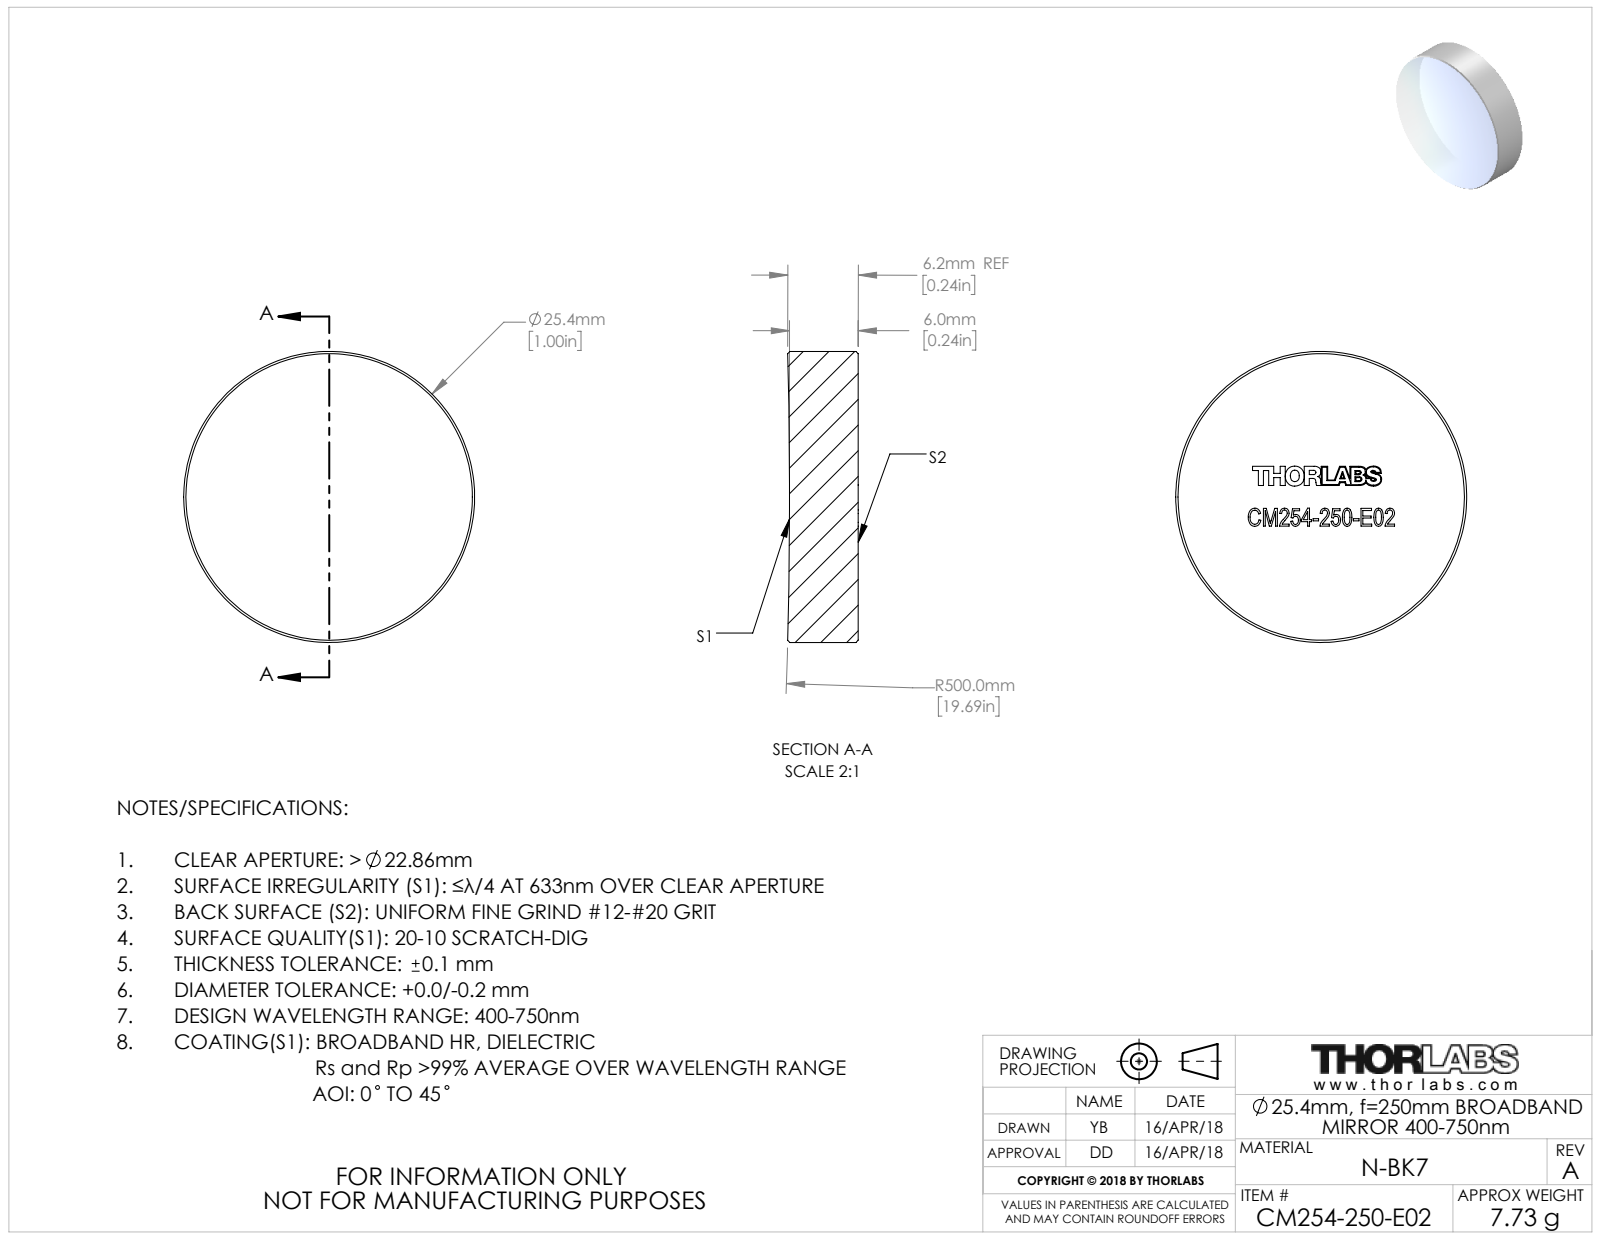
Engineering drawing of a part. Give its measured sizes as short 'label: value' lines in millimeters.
name: TTN153299-E0W
written by: SolidWorks 2018 (CONFIG_CONTROL_DESIGN)
unit: mm
bodies: 1 solid, 40 faces (32 planar, 2 cylindrical, 6 other)
size: 25.4 × 25.4 × 6.16
volume: 3 078 mm³; area: 1 486 mm²
bosses: 1× ⌀25.4
